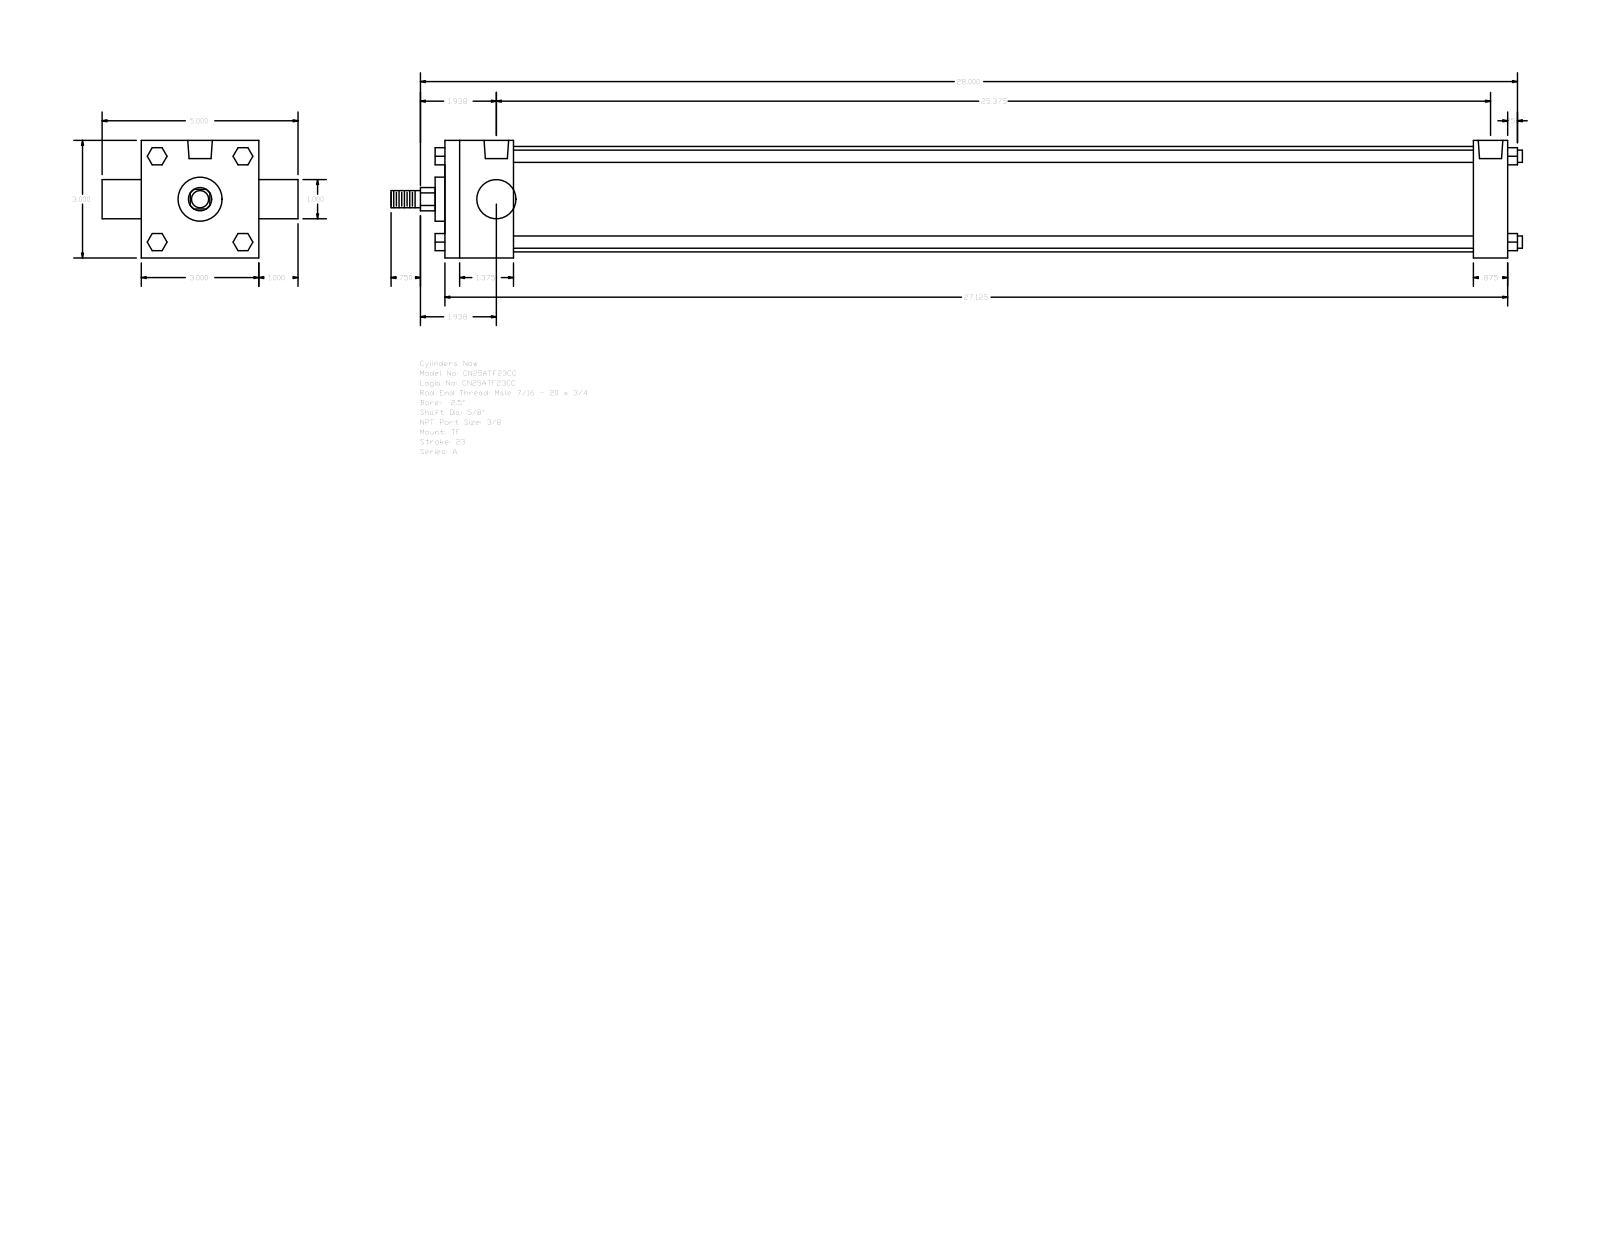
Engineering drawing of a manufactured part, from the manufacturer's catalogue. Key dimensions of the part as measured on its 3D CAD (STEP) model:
Part name (STEP PRODUCT): A_TF__0250_0.625
STEP written by: GSSL Pune (CONFIG_CONTROL_DESIGN)
Units: millimetres
Bodies: 0 solids, 120 faces (92 planar, 28 cylindrical, 0 other)
Overall size (bounding box): 733.42 × 127 × 76.2
Round holes (diameter × count): ⌀5.56 ×3, ⌀15.93 ×2
Round bosses / shafts (diameter × count): ⌀7.94 ×4, ⌀68.33 ×1, ⌀28.57 ×1, ⌀25.4 ×1, ⌀15.88 ×1, ⌀11.11 ×1
Partial cylindrical surfaces — rounded edges, fillets, slot ends (radius × count): R7.54 ×1
Main face-to-face distances: 76.2, 688.97, 44.45, 666.74, 622.29, 644.52, 22.23, 25.4, 101.6, 6.35
Hole centre spacings: 2.38, 646.91, 644.53, 649.29
